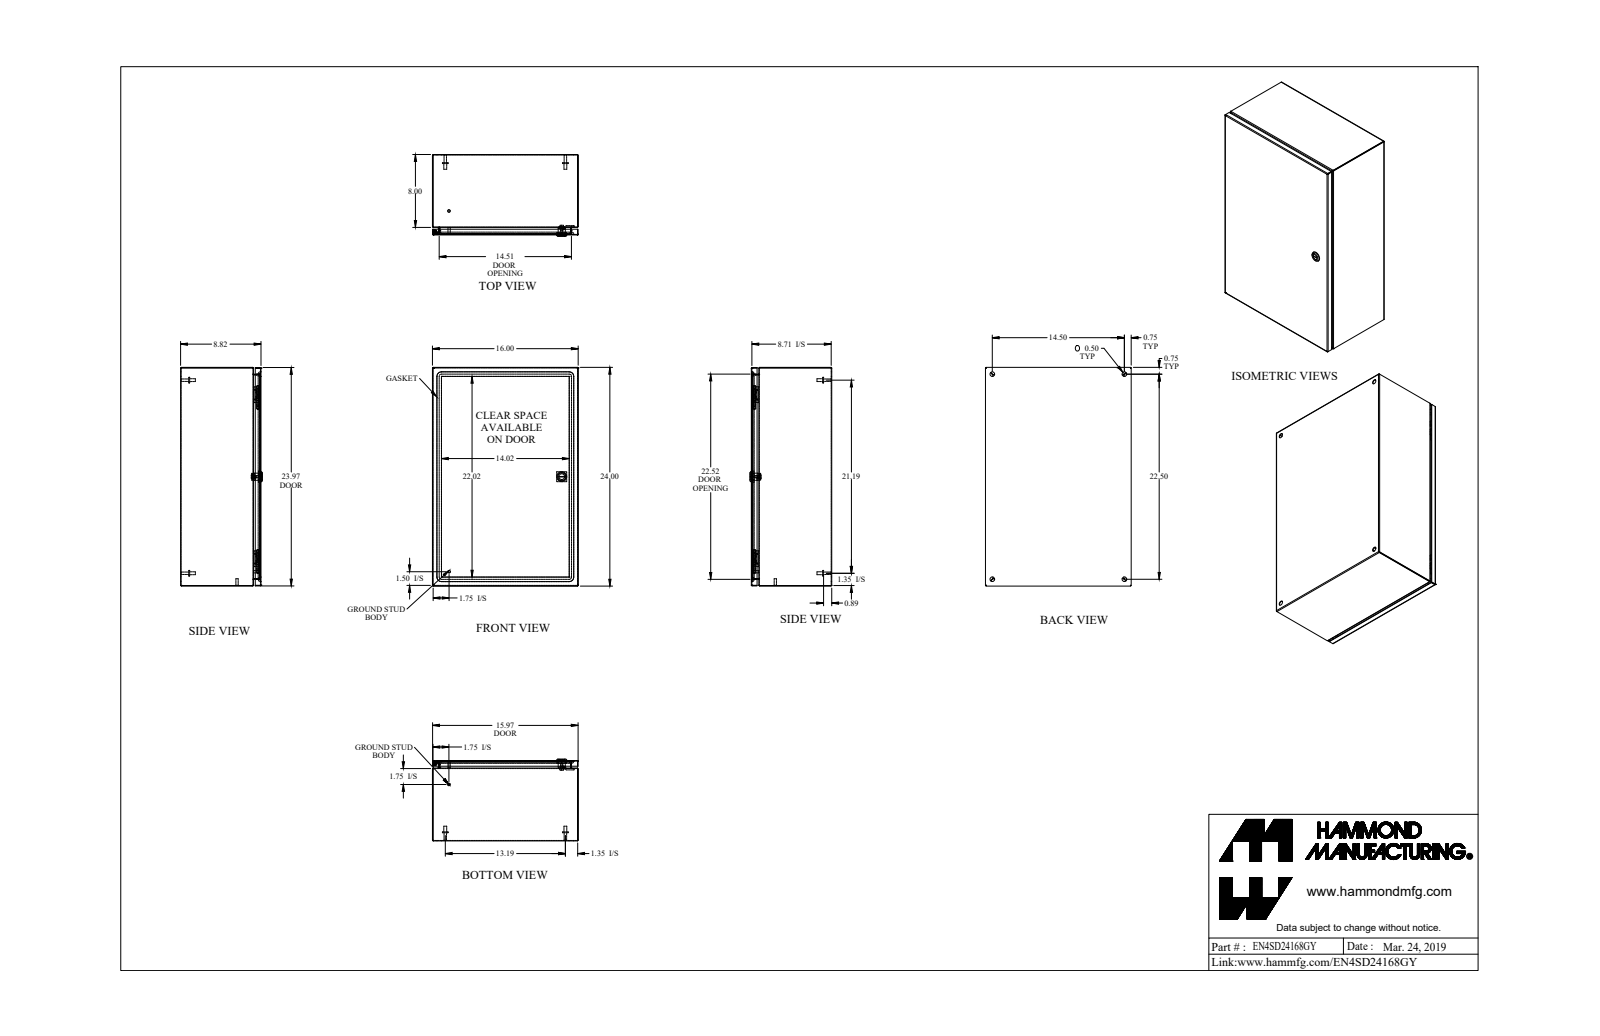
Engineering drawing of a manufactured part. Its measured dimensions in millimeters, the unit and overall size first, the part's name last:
Units: millimetres
Overall size (bounding box): 609.6 × 406.4 × 228.1
Round holes (diameter × count): ⌀12.7 ×4, ⌀4.4 ×1, ⌀5.9 ×1, ⌀6.1 ×1, ⌀6.1 ×1, ⌀15.9 ×1, ⌀19.9 ×1
Round bosses / shafts (diameter × count): ⌀15.9 ×4, ⌀8 ×4, ⌀6.9 ×4, ⌀7.1 ×2, ⌀6.4 ×2, ⌀27.9 ×1, ⌀13.3 ×1, ⌀11.6 ×1
Partial cylindrical surfaces — rounded edges, fillets, slot ends (radius × count): R0.7 ×21, R2.2 ×21, R6.4 ×16, R482.6 ×8, R0.2 ×4, R1.6 ×4, R12.7 ×4, R3.2 ×2
Main face-to-face distances: 1.4, 222.6, 221.2, 224.1, 405, 608.2, 403.5, 406.4, 606.7, 609.6
Hole centre spacings: 368.3, 571.5, 679.9, 287, 287, 445.2, 445.2
Volume: 1 589 000 mm³ · Surface area: 2 132 000 mm²
Bodies: 21 solids, 634 faces (285 planar, 213 cylindrical, 136 other)
Part name (STEP PRODUCT): EN4SD24168GY_Default
STEP written by: SolidWorks 2019 (CONFIG_CONTROL_DESIGN)
